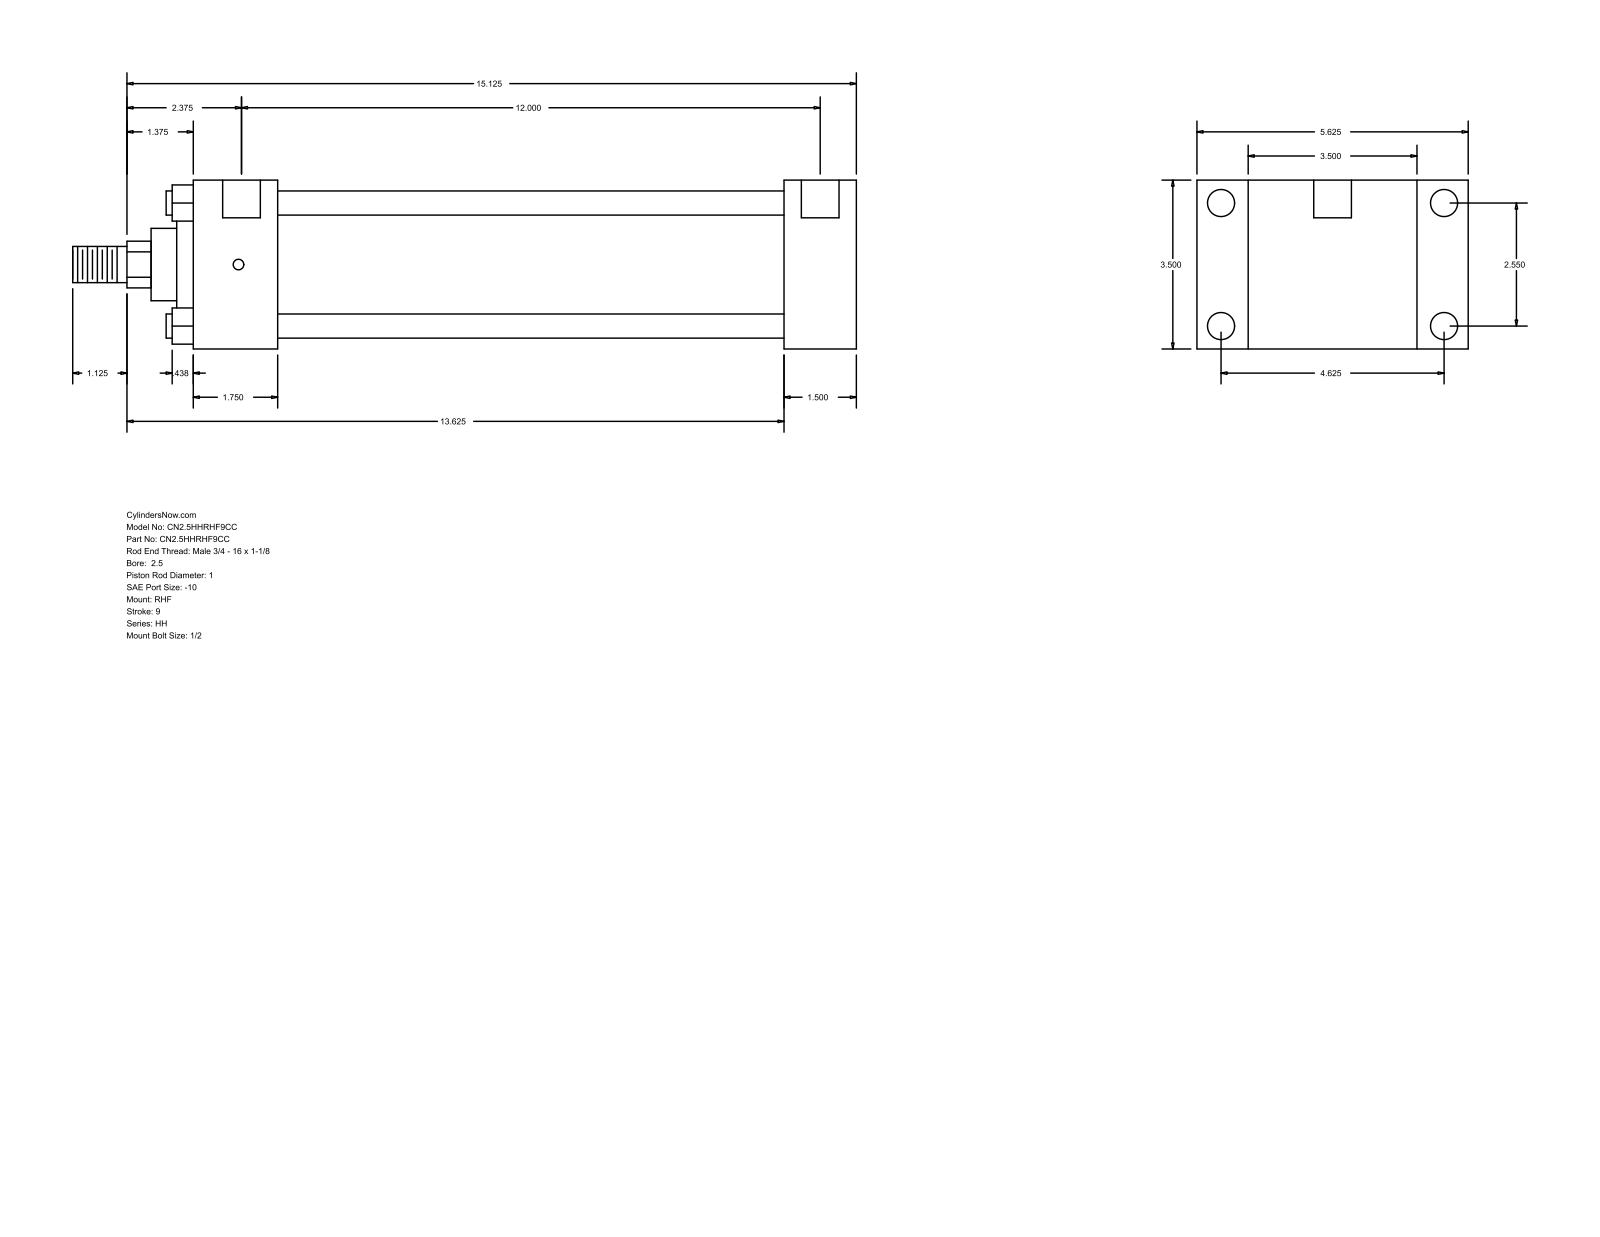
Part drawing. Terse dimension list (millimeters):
name: HH_RHF__0250_1
written by: GSSL Pune (CONFIG_CONTROL_DESIGN)
unit: mm
bodies: 0 solids, 90 faces (61 planar, 29 cylindrical, 0 other)
size: 412.75 × 142.88 × 88.9
holes: 4× ⌀5.56, 4× ⌀14.3, 2× ⌀19.84
bosses: 4× ⌀12.7, 1× ⌀73.03, 1× ⌀60.33, 1× ⌀38.1, 1× ⌀25.4, 1× ⌀19.05
rounds: 1× R12.29
face distances: 88.9, 38.11, 26.99, 115.89, 311.15, 349.26, 142.88, 44.46, 266.69, 304.8
hole spacings: 1.59, 64.76, 117.48, 134.15, 306.38, 307.97, 304.79
